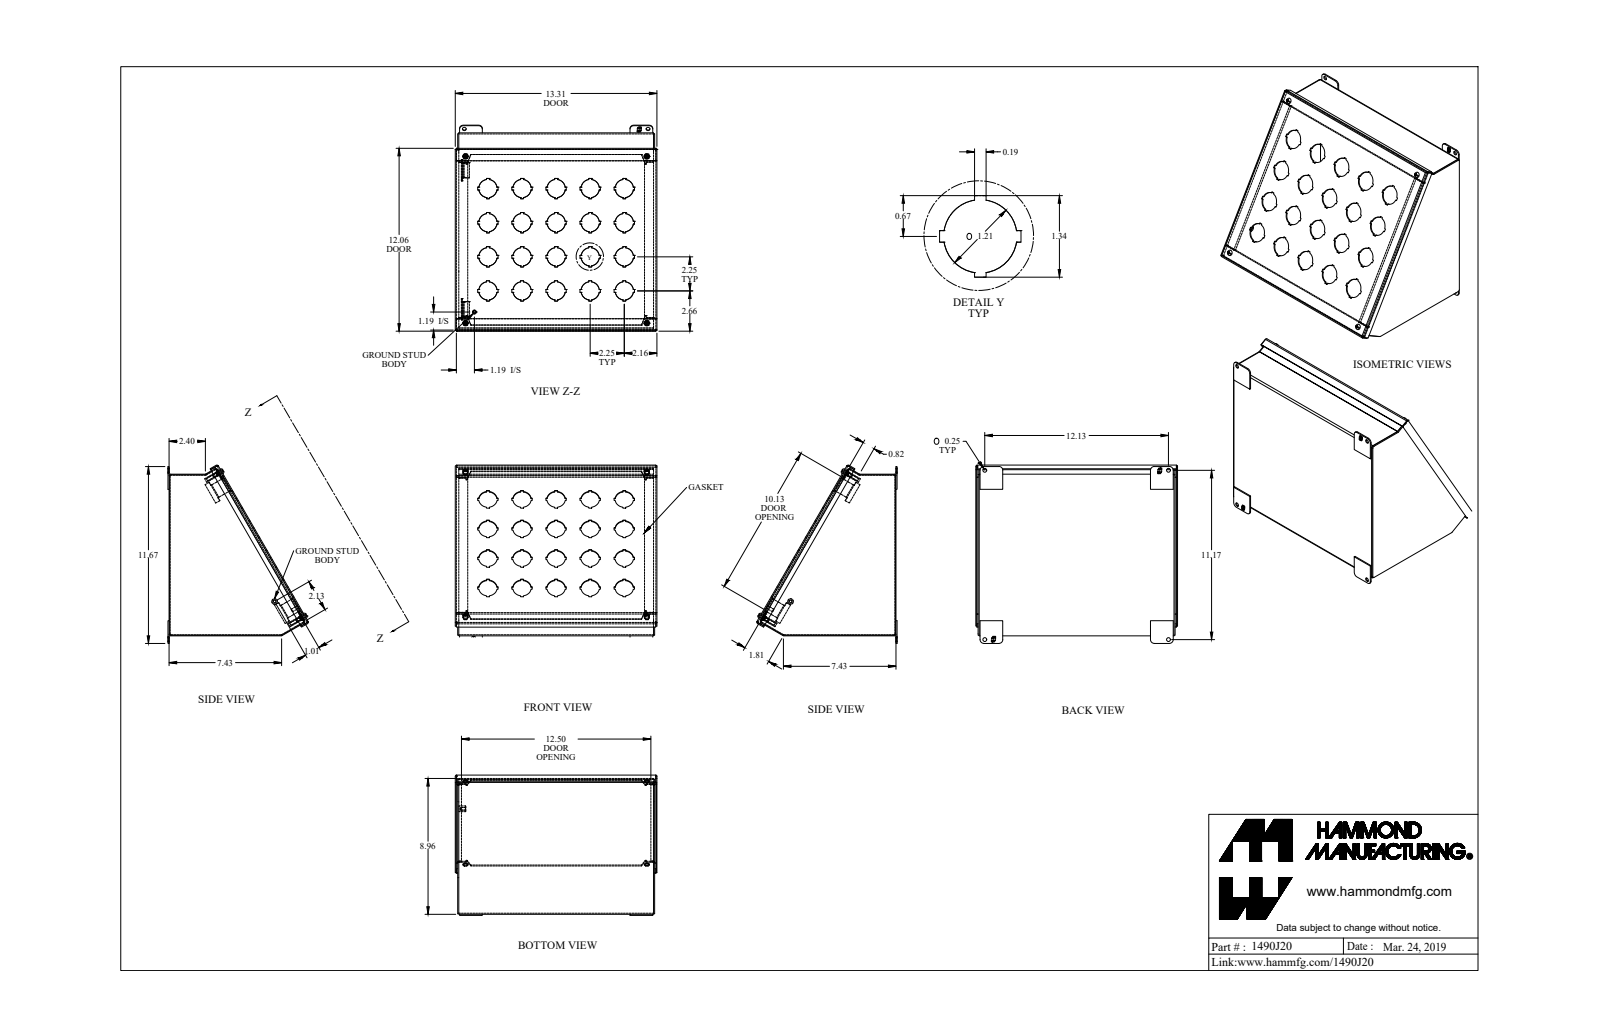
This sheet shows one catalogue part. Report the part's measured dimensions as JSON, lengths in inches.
{"part_name": "1490J20_Default", "step_written_by": "SolidWorks 2019 (CONFIG_CONTROL_DESIGN)", "units": "inches", "bodies": {"solids": 28, "faces": 1028, "planar": 745, "cylindrical": 243, "other": 40}, "overall_size": [13.312, 11.766, 9.258], "volume_in3": 50.73, "surface_area_in2": 1343, "round_holes": [[1.21, 20], [0.25, 8], [0.159, 4], [0.156, 1]], "round_bosses_or_shafts": [[0.39, 4], [0.275, 4], [0.19, 4], [0.148, 4], [0.375, 1], [0.25, 1], [0.188, 1]], "partial_cylinders_radius": [[0.108, 18], [0.036, 12], [0.029, 8], [0.086, 8], [0.25, 8], [0.125, 4], [0.16, 4], [0.171, 4]], "face_to_face_distances": [0.072, 12.928, 12.856, 13, 10.595, 0.259, 0.187, 10.667, 10.523, 11.678], "hole_center_spacings": [5.031, 2.25, 3.182, 4.5, 8.113, 6.75, 6.364, 7.115]}
